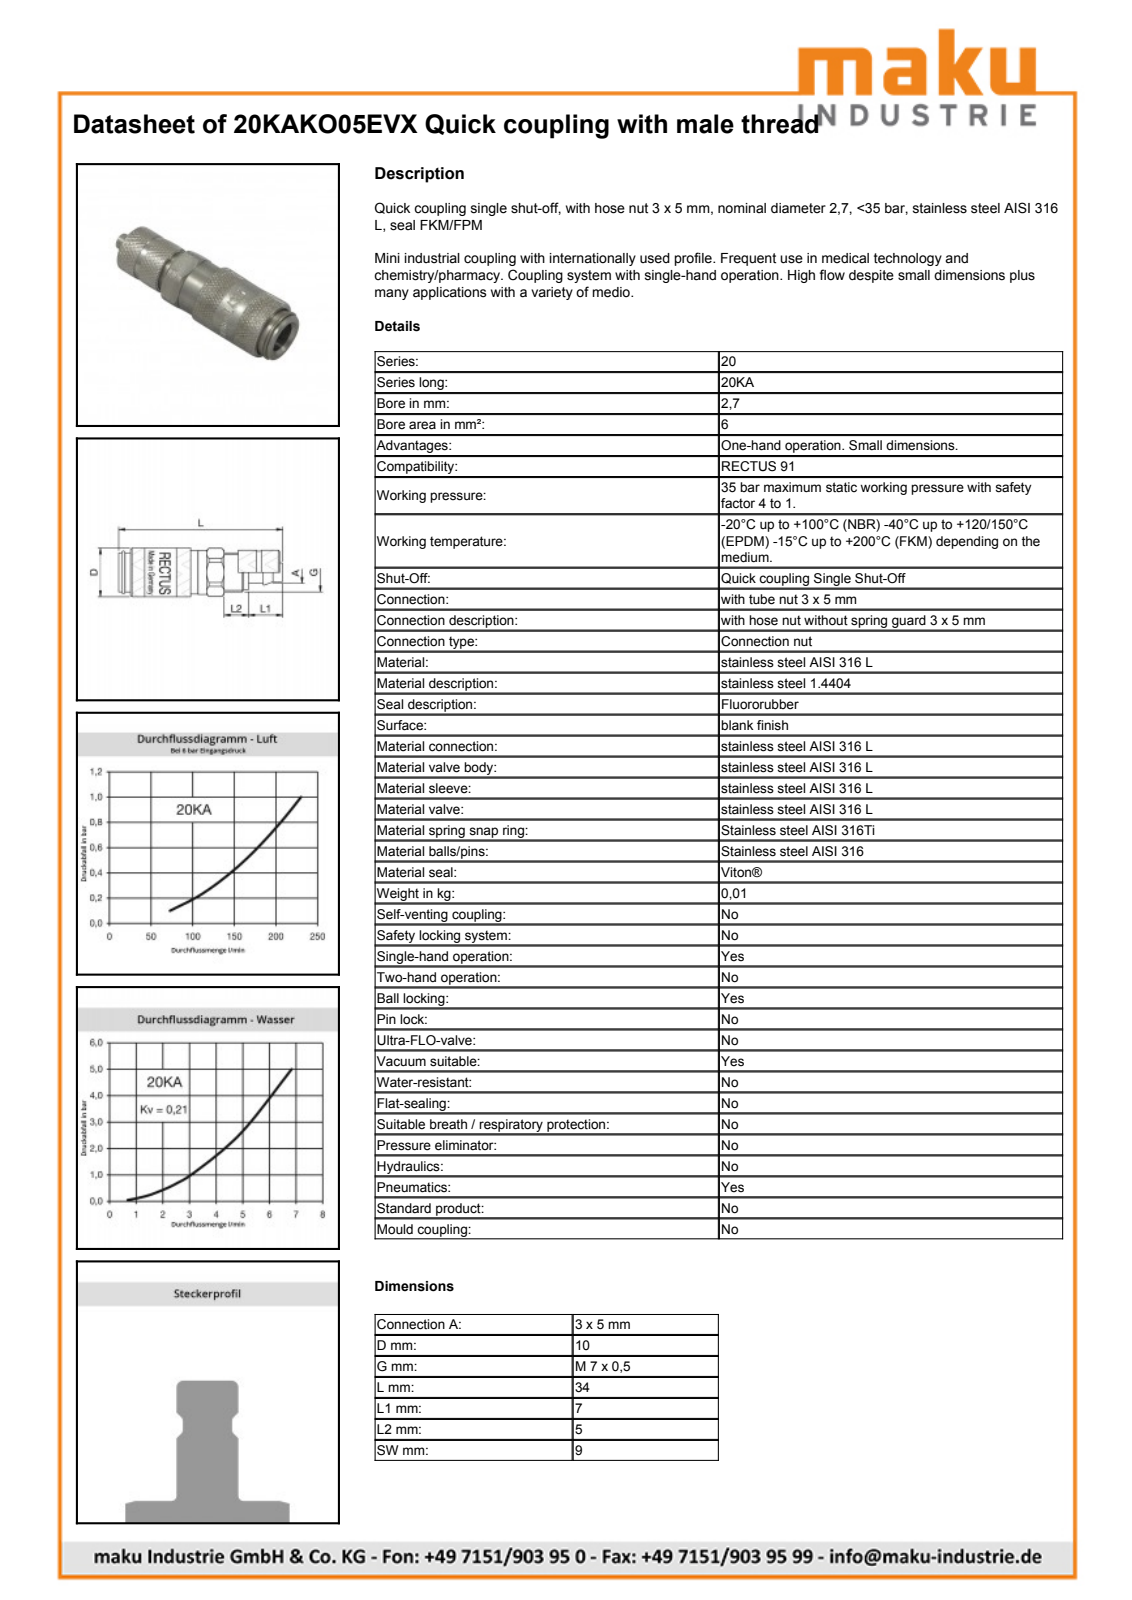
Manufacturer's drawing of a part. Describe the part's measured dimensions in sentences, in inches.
The part is named "D108538". Its 3-D file was written by "Autodesk Inventor 2013 (AUTOMOTIVE_DESIGN)". It is 2 solids with 484 faces: 165 planar, 78 cylindrical and 241 other. Overall it measures 1.321 by 0.407 by 0.407 inches. Its volume is 0.111 cubic inches and its surface area 3.891 square inches. Round holes: 1 of diameter 0.207, 1 of diameter 0.248, 1 of diameter 0.254, 1 of diameter 0.256, 1 of diameter 0.276, 1 of diameter 0.294, 1 of diameter 0.321, 1 of diameter 0.36, 1 of diameter 0.362. Round bosses or shafts: 1 of diameter 0.407, 1 of diameter 0.394, 1 of diameter 0.354, 1 of diameter 0.35, 1 of diameter 0.319, 1 of diameter 0.315, 1 of diameter 0.307, 1 of diameter 0.303. Partial cylindrical surfaces (rounded edges, fillets, slot ends): 1 of radius 0.193, 1 of radius 0.195. The main face-to-face distances are 0.354, 0.197, 0.482, 0.848, 0.709, 0.146, 0.337, 0.14, 0.563, 0.079.
